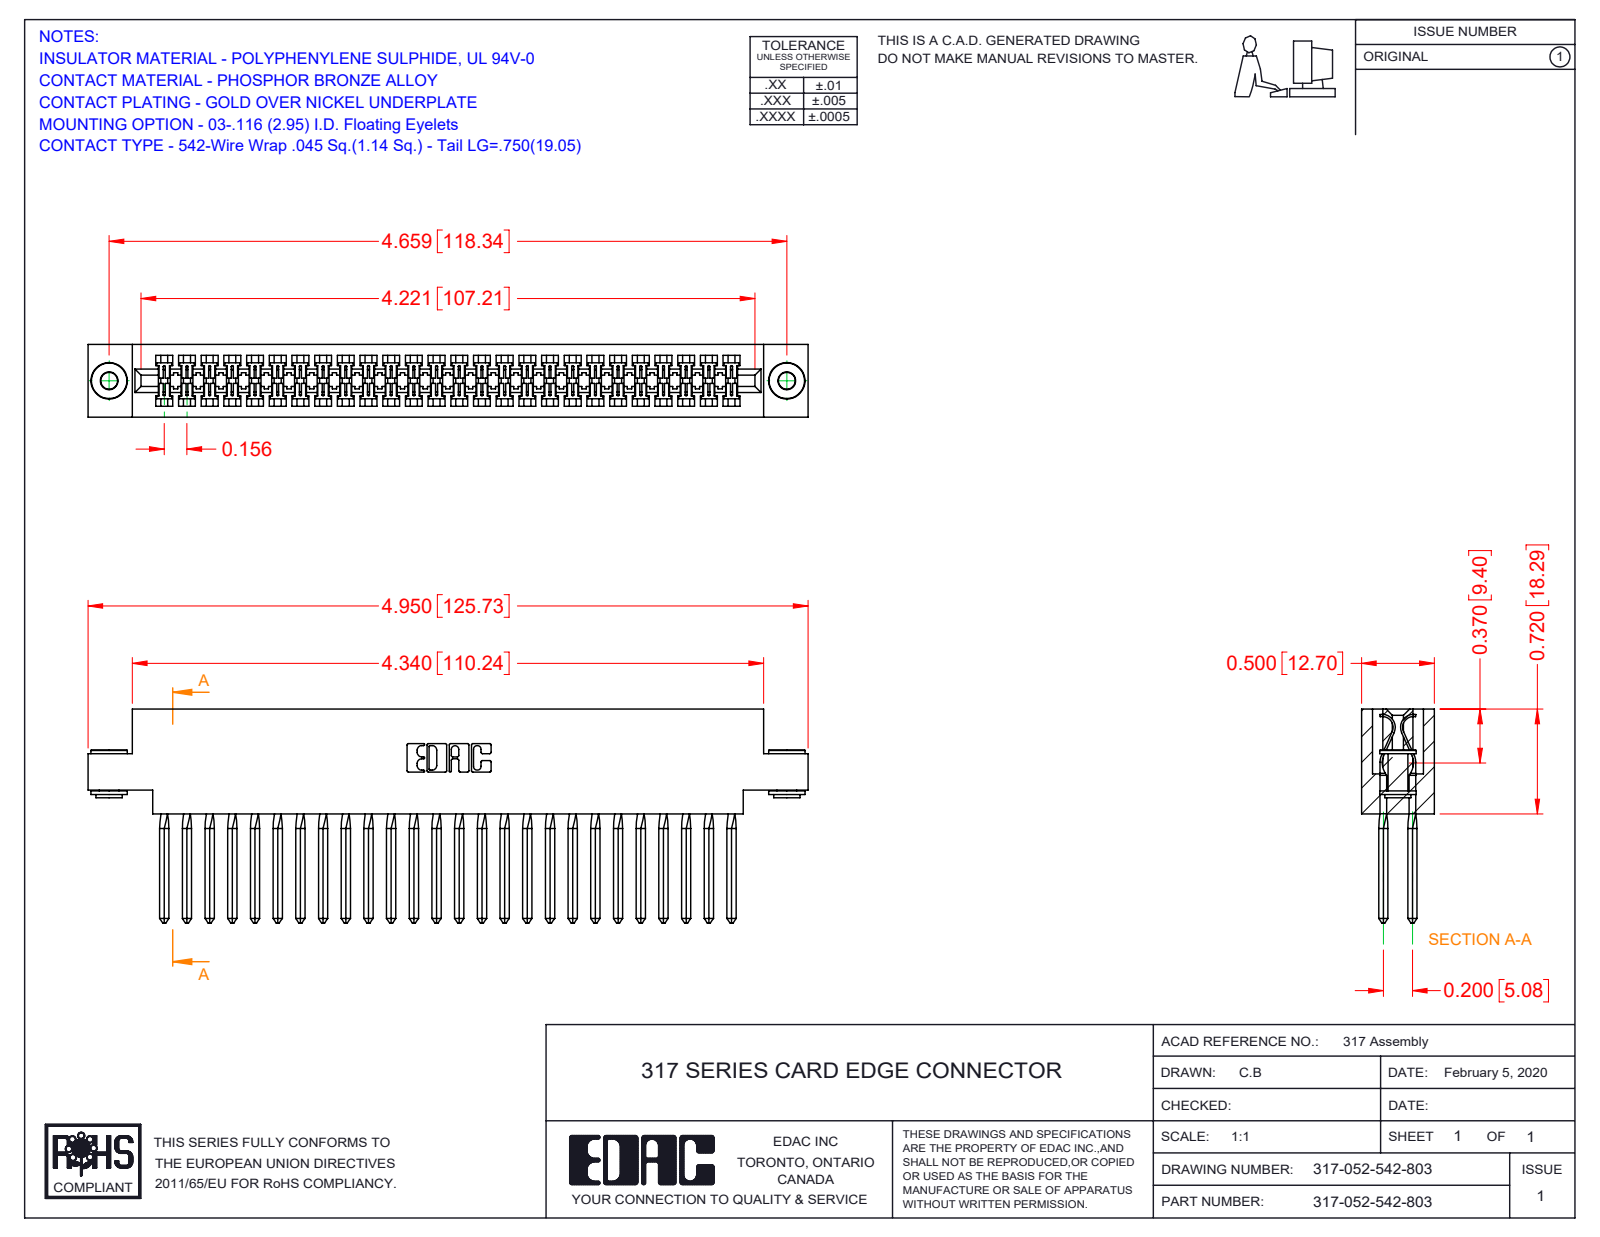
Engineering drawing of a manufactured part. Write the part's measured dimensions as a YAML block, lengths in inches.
part_name: "317-052-542-803; 317-290-003_542; 317 Part_.156 Dia - TH; 345-250-002_345-250-002-102"
step_written_by: "SolidWorks 2016 (CONFIG_CONTROL_DESIGN)"
units: inches
bodies: {solids: 55, faces: 3104, planar: 2460, cylindrical: 428, other: 216}
overall_size: [4.95, 1.47, 0.5]
volume: 1.227
surface_area: 42.87
round_holes:
  - {diameter: 0.116, count: 2}
  - {diameter: 0.156, count: 2}
round_bosses_or_shafts:
  - {diameter: 0.25, count: 2}
  - {diameter: 0.18, count: 2}
  - {diameter: 0.136, count: 2}
partial_cylinders:
  - {radius: 0.006, count: 104}
  - {radius: 0.01, count: 22}
  - {radius: 0.007, count: 6}
  - {radius: 0.031, count: 6}
  - {radius: 0.026, count: 3}
  - {radius: 0.074, count: 2}
  - {radius: 0.089, count: 2}
  - {radius: 0.1, count: 2}
face_to_face_distances: [0.5, 0.075, 0.425, 0.35, 0.2, 0.11, 0.116, 0.046, 0.72, 0.136]
hole_center_spacings: [4.659]
